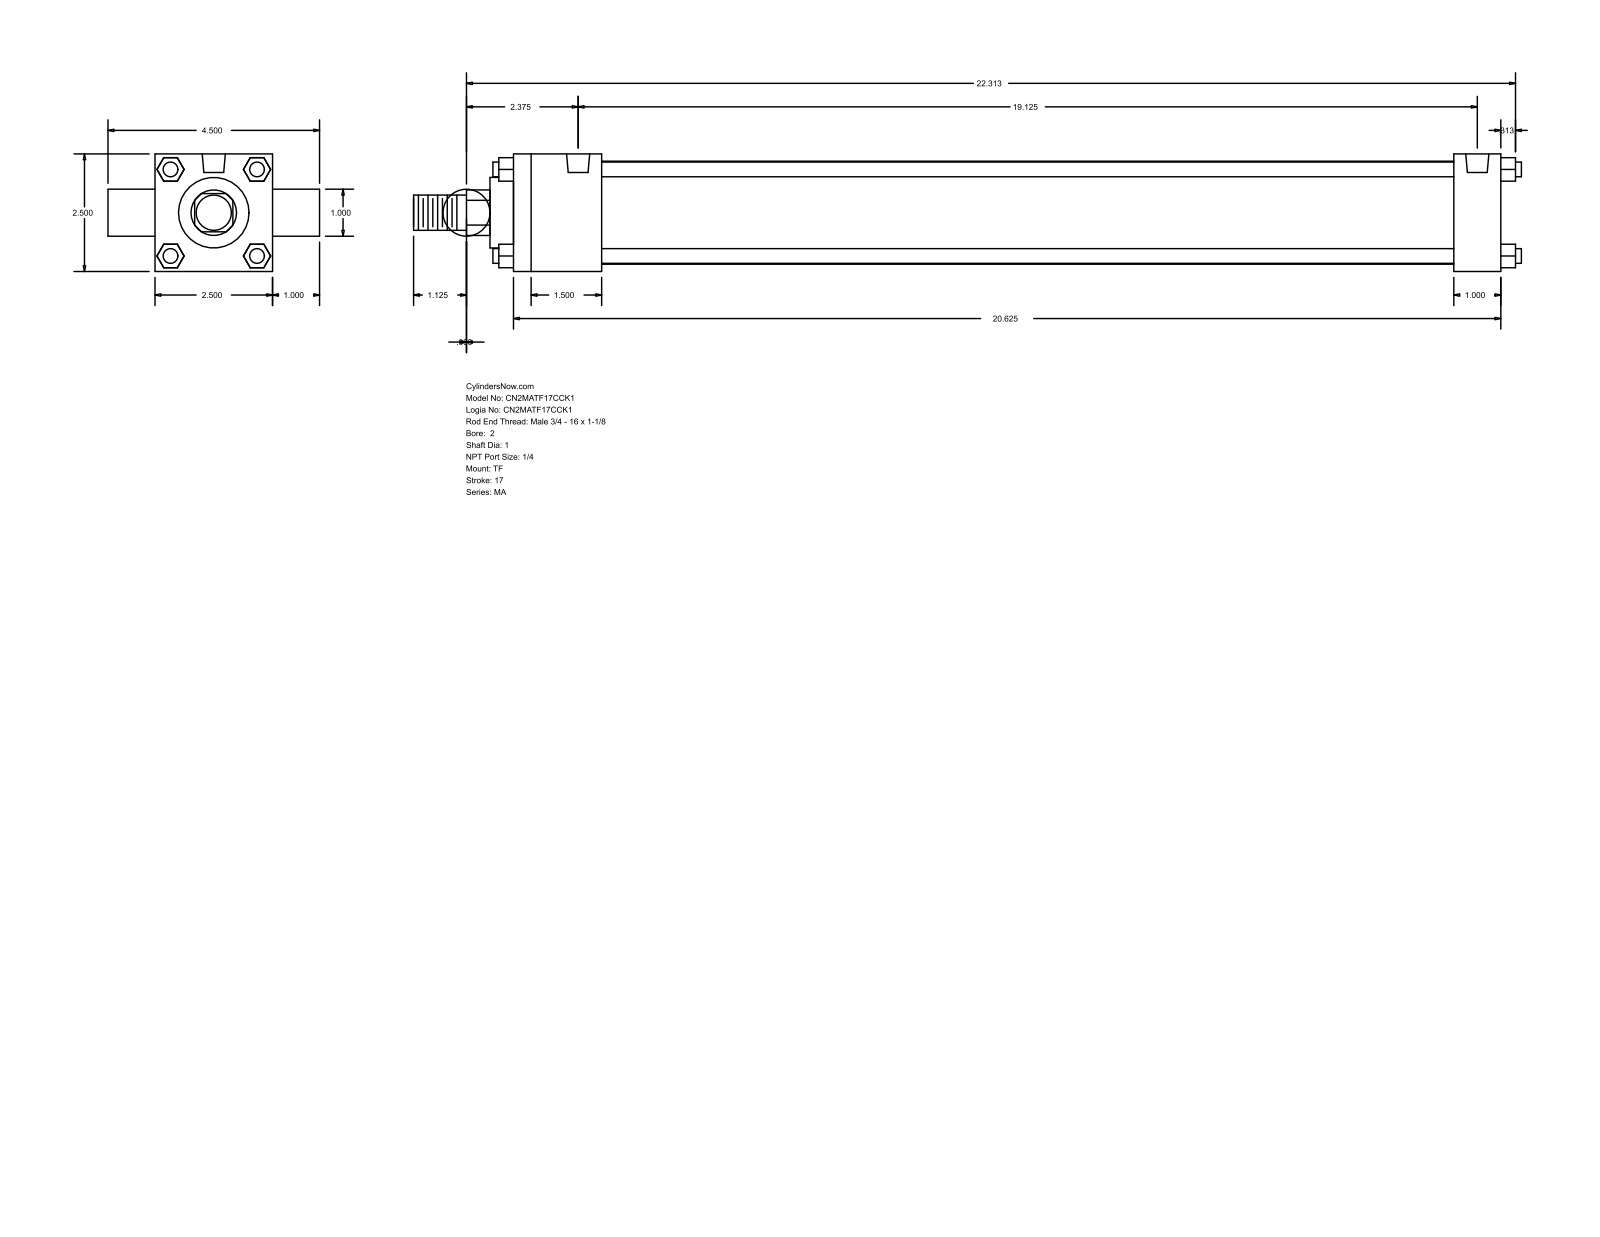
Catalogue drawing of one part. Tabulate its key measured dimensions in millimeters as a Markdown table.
| quantity | value |
| --- | --- |
| part name | MA_TF__0200_1 |
| STEP written by | GSSL Pune (CONFIG_CONTROL_DESIGN) |
| units | millimeters |
| bodies | 0 solids, 120 faces (92 planar, 28 cylindrical, 0 other) |
| overall size | 598.49 × 114.3 × 63.5 |
| round holes (diameter × count) | 7.94 × 3, 12.49 × 2 |
| round bosses / shafts (diameter × count) | 7.94 × 4, 25.4 × 2, 55.63 × 1, 38.1 × 1, 19.05 × 1 |
| partial cylindrical surfaces (radius × count) | 12.29 × 1 |
| main face-to-face distances | 63.5, 25.4, 533.4, 12.7, 47.63, 508, 460.37, 485.77, 88.9, 40.47 |
| hole center spacings | 485.77 |
